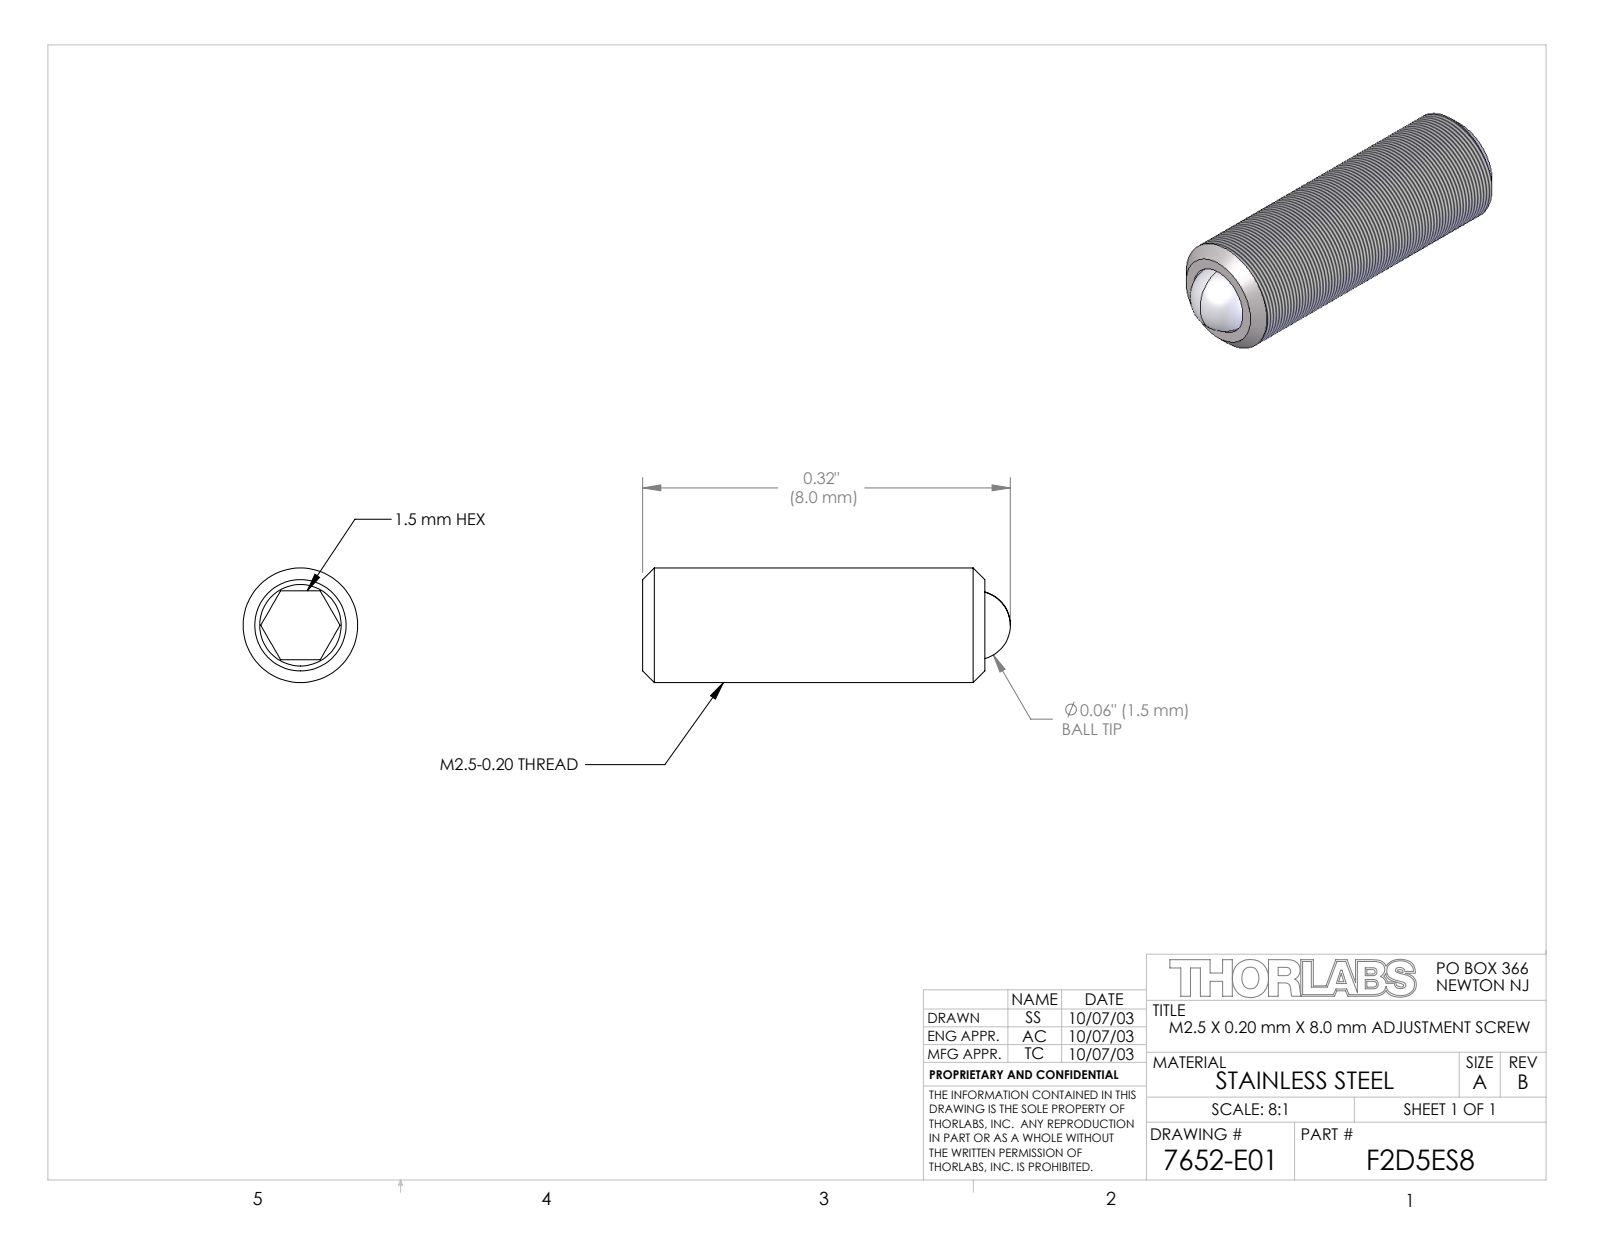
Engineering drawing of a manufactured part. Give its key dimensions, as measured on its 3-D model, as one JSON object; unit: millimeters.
{"part_name": "7652-E0W", "step_written_by": "SolidWorks 2018 (AUTOMOTIVE_DESIGN)", "units": "millimeters", "bodies": {"solids": 2, "faces": 25, "planar": 9, "cylindrical": 4, "other": 12}, "overall_size": [8, 2.5, 2.5], "volume_mm3": 30, "surface_area_mm2": 92, "round_holes": [[1.5, 1]], "round_bosses_or_shafts": [[2.5, 1]], "face_to_face_distances": [1.5, 4.4, 3, 7.5]}
